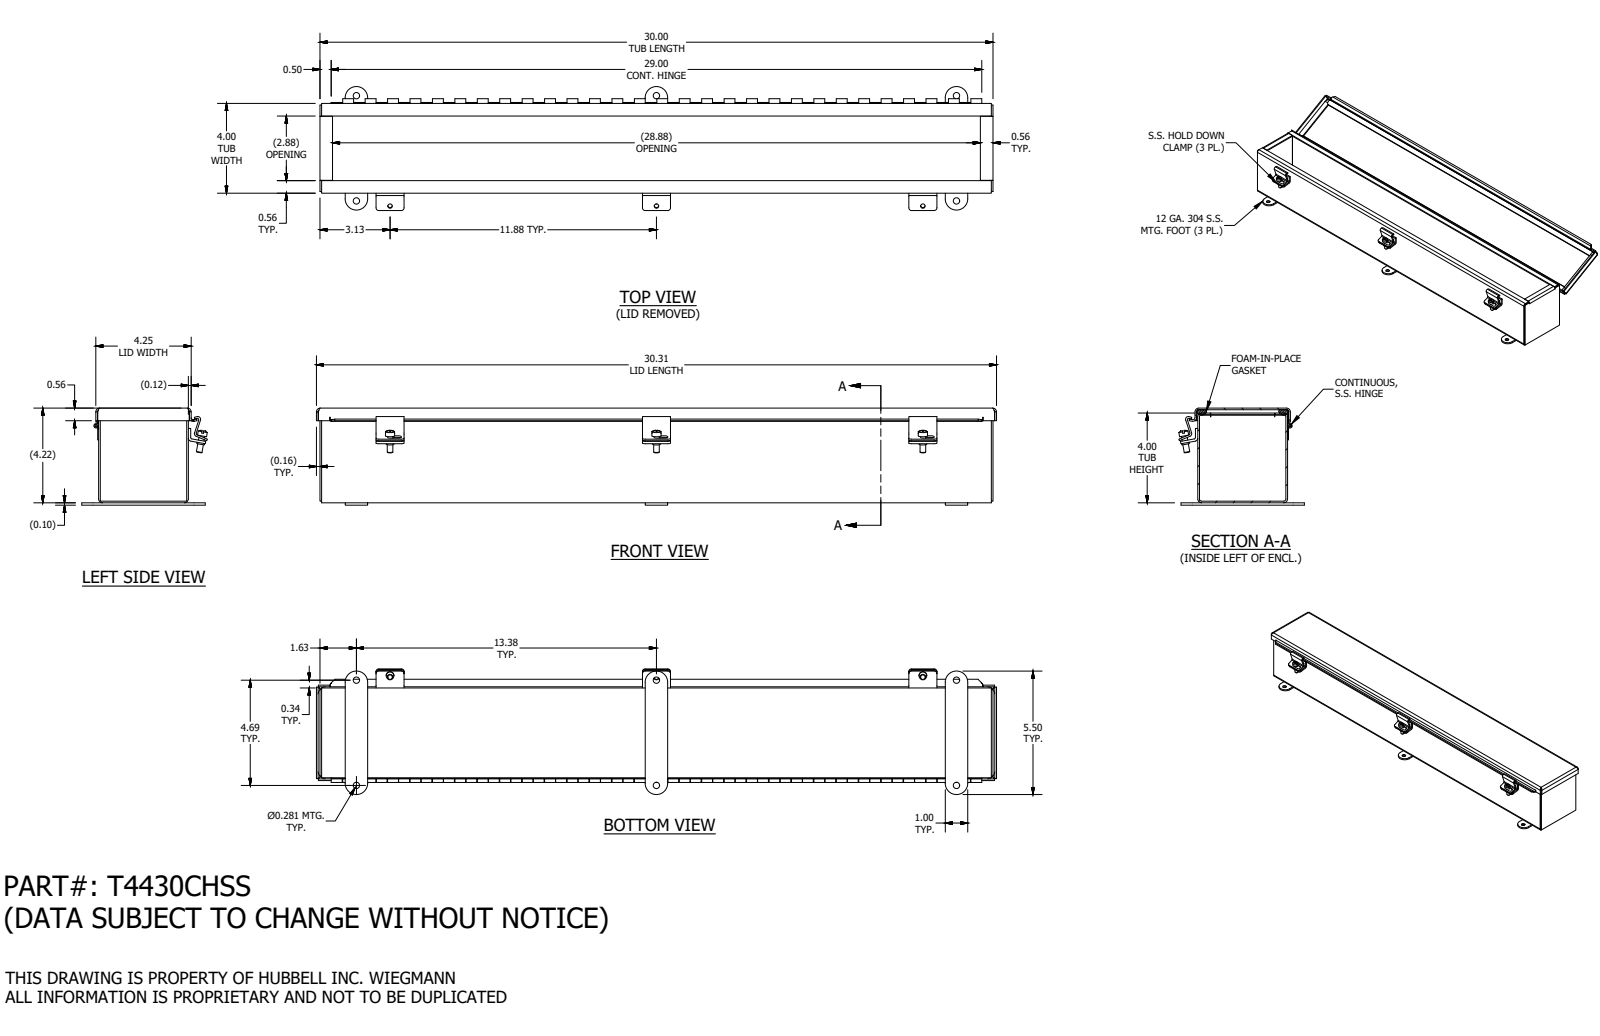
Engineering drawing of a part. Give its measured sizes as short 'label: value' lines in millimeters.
name: T4430CHSS
written by: SolidWorks 2019 (AUTOMOTIVE_DESIGN)
unit: mm
bodies: 20 solids, 659 faces (395 planar, 225 cylindrical, 39 other)
size: 770 × 142.2 × 109.8
volume: 870 600 mm³; area: 909 000 mm²
holes: 6× ⌀2.8, 6× ⌀7.1, 3× ⌀5, 1× ⌀2.9
bosses: 3× ⌀10.4, 3× ⌀8.7, 3× ⌀6.4, 1× ⌀5.1, 1× ⌀2.5
rounds: 12× R3.2, 11× R2.4, 11× R4.3, 8× R2.2, 6× R3.4, 6× R12.7, 4× R6.1, 3× R1.6
face distances: 1.9, 99.7, 105.3, 101.6, 97.8, 107.1, 103.4, 5.5, 102.9, 3.2
hole spacings: 301.6, 339.7, 360, 19.1, 119, 301.6, 603.3, 679.5
